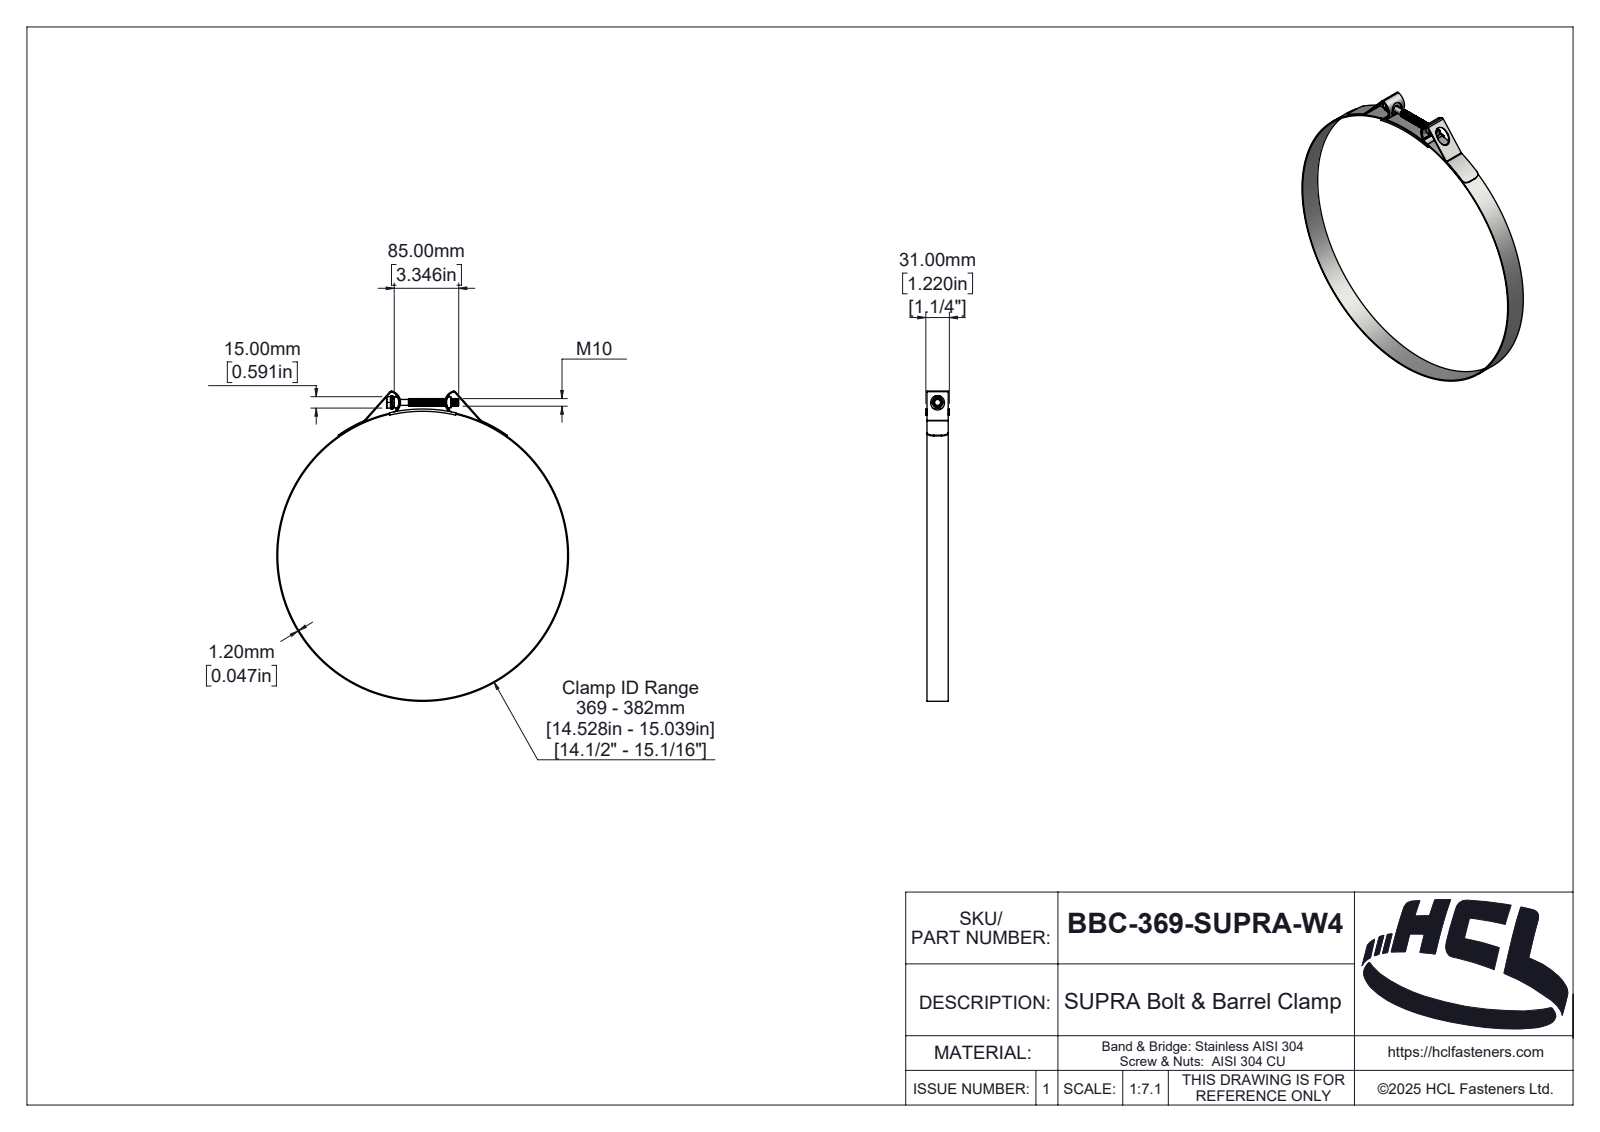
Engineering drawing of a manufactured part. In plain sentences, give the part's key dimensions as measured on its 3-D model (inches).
The part is named "BBC-369-SUPRA-W4". Its 3-D file was written by "SolidWorks 2025 (AUTOMOTIVE_DESIGN)". It is 5 solids with 377 faces: 50 planar, 241 cylindrical and 86 other. Overall it measures 16.089 by 15.134 by 1.22 inches. Its volume is 3.534 cubic inches and its surface area 143.6 square inches. Round holes: 1 of diameter 15.039. Round bosses or shafts: 1 of diameter 15.134, 1 of diameter 0.682, 1 of diameter 0.551, 1 of diameter 0.394, 1 of diameter 0.307. Partial cylindrical surfaces (rounded edges, fillets, slot ends): 4 of radius 0.039, 2 of radius 0.051, 2 of radius 0.079, 2 of radius 0.098, 2 of radius 0.126, 2 of radius 0.354, 2 of radius 0.515, 2 of radius 0.554. The main face-to-face distances are 0.047, 1.102, 0.059, 1.161, 1.173, 1.114, 1.22, 0.492, 3.248, 1.126.
